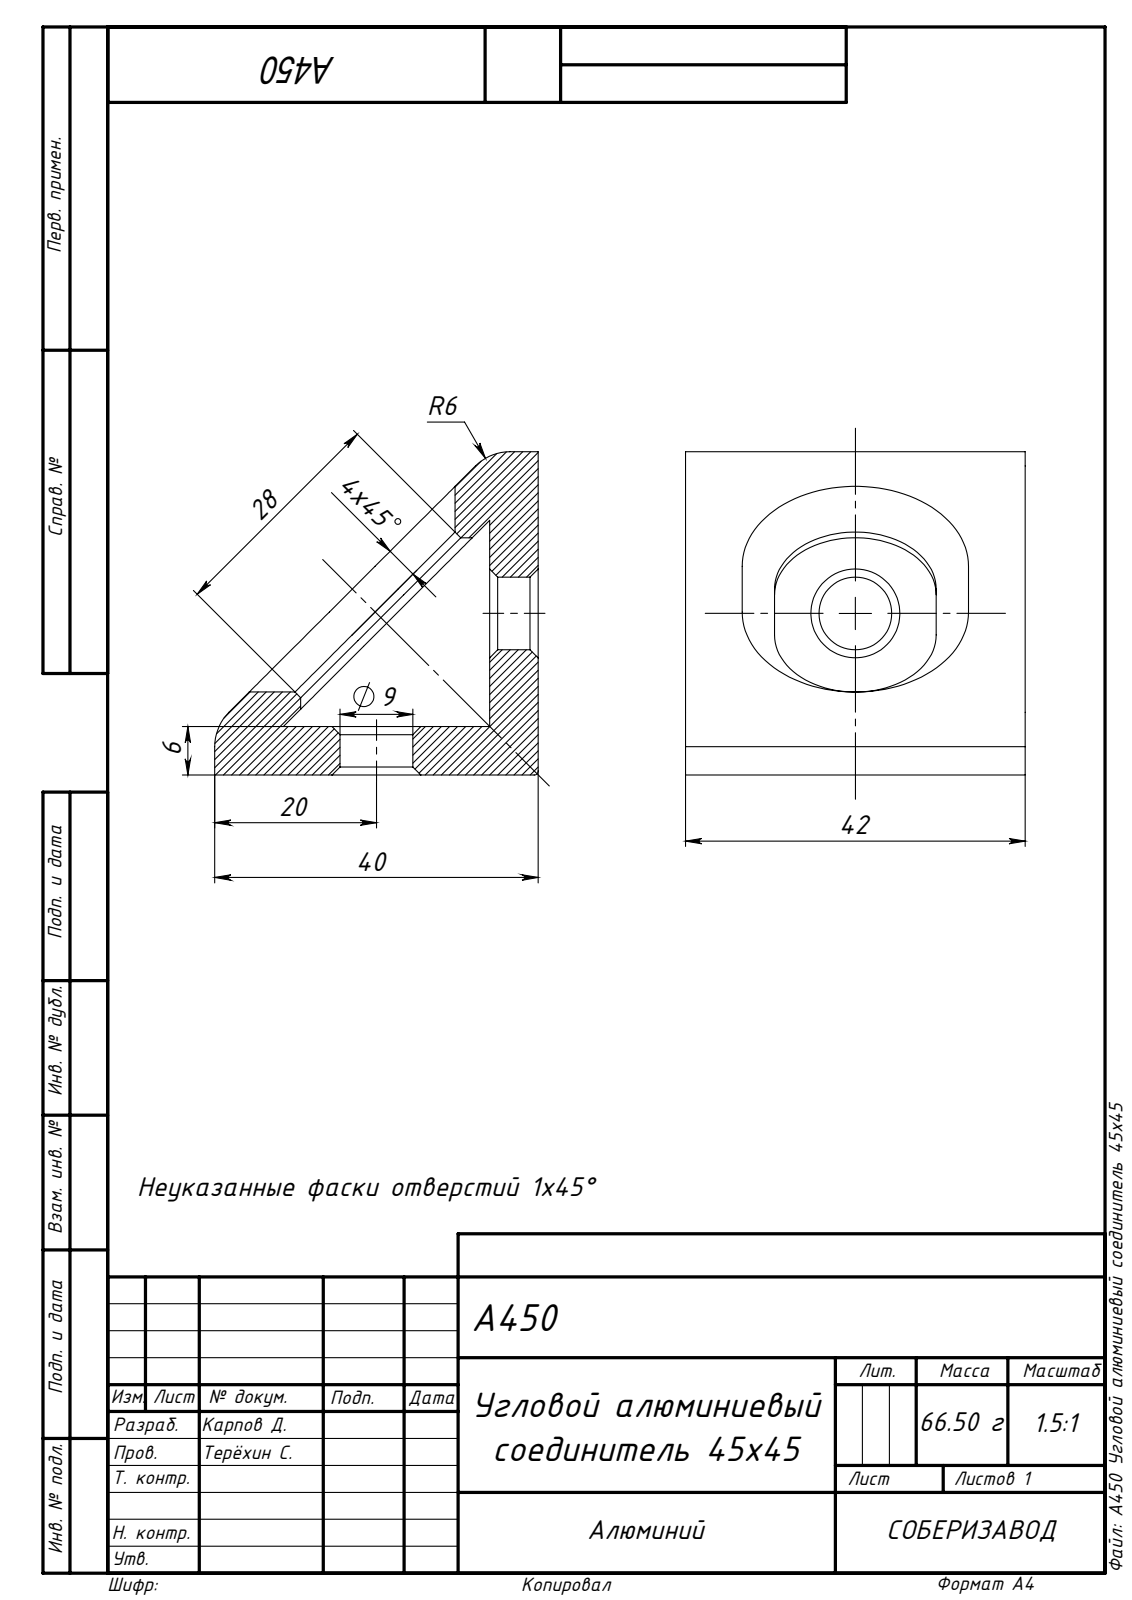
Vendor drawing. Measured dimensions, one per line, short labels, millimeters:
name: A450 Угловой алюминиевый соединитель 45х45
written by: SolidWorks 2021 (AUTOMOTIVE_DESIGN)
unit: mm
bodies: 1 solid, 40 faces (16 planar, 10 cylindrical, 14 other)
size: 42 × 40 × 40
volume: 24 855 mm³; area: 10 292 mm²
holes: 2× ⌀9
rounds: 2× R6, 2× R10, 1× R0.5
face distances: 6, 42, 40, 34, 11, 31, 20, 13.08
